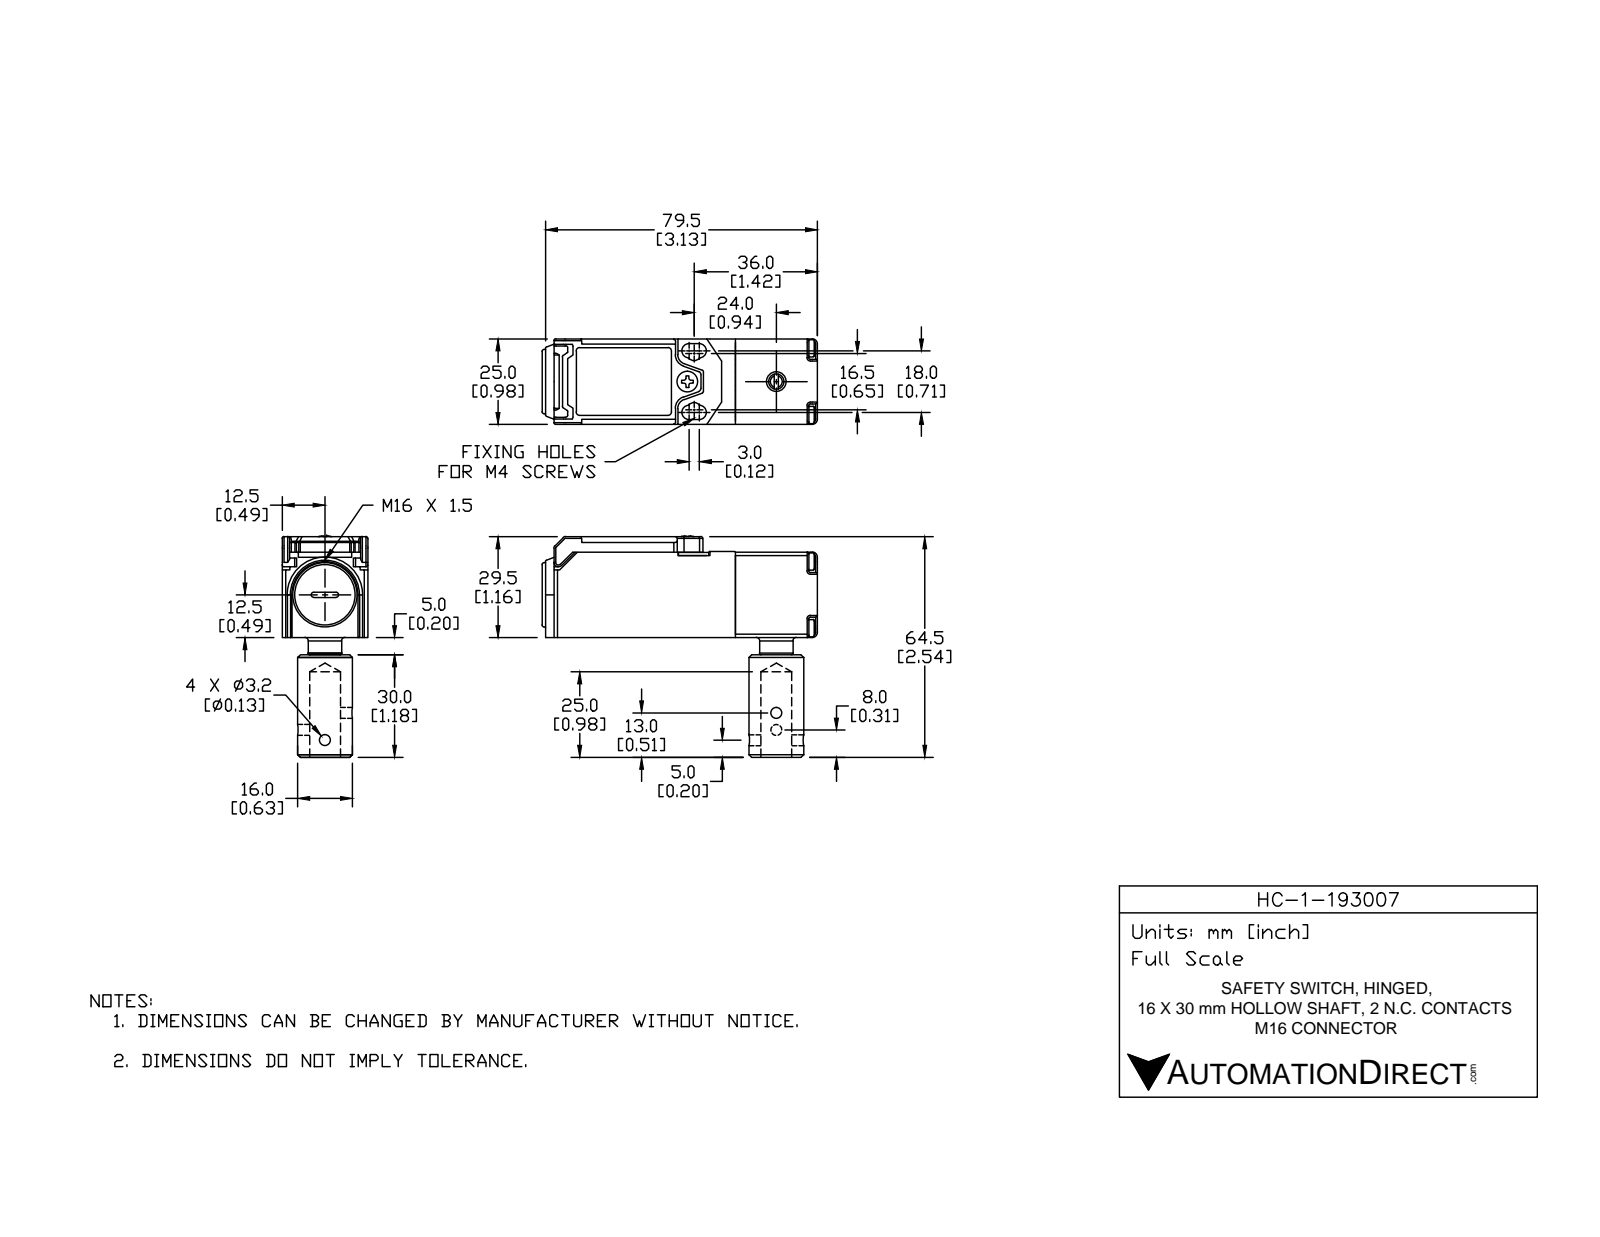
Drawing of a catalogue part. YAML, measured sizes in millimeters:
part_name: "HC-1-193007"
step_written_by: "SolidWorks 2014 (AUTOMOTIVE_DESIGN)"
units: millimeters
bodies: {solids: 14, faces: 1716, planar: 700, cylindrical: 611, other: 405}
overall_size: [80.5, 64.7, 25]
volume: 29430
surface_area: 28750
round_holes:
  - {diameter: 3.2, count: 8}
  - {diameter: 2.4, count: 4}
  - {diameter: 1.5, count: 2}
  - {diameter: 1.6, count: 2}
  - {diameter: 1.8, count: 2}
  - {diameter: 2.2, count: 2}
  - {diameter: 3.6, count: 2}
  - {diameter: 1.4, count: 1}
  - {diameter: 2.1, count: 1}
  - {diameter: 2.5, count: 1}
  - {diameter: 2.6, count: 1}
  - {diameter: 4.7, count: 1}
round_bosses_or_shafts:
  - {diameter: 2.6, count: 5}
  - {diameter: 5, count: 4}
  - {diameter: 2, count: 4}
  - {diameter: 3.5, count: 2}
  - {diameter: 18.8, count: 1}
  - {diameter: 16, count: 1}
  - {diameter: 13.5, count: 1}
  - {diameter: 9.8, count: 1}
partial_cylinders:
  - {radius: 0.5, count: 226}
  - {radius: 0.1, count: 24}
  - {radius: 0.3, count: 20}
  - {radius: 1, count: 20}
  - {radius: 1.5, count: 7}
  - {radius: 2.1, count: 6}
  - {radius: 2.8, count: 6}
  - {radius: 0.2, count: 4}
face_to_face_distances: [25, 2, 1.8, 23.2, 1, 23, 24, 21, 22.2, 29.2]
hole_center_spacings: [13.8, 19.5, 4.3, 4.7, 6.2, 10.5, 10.7, 10.8]
